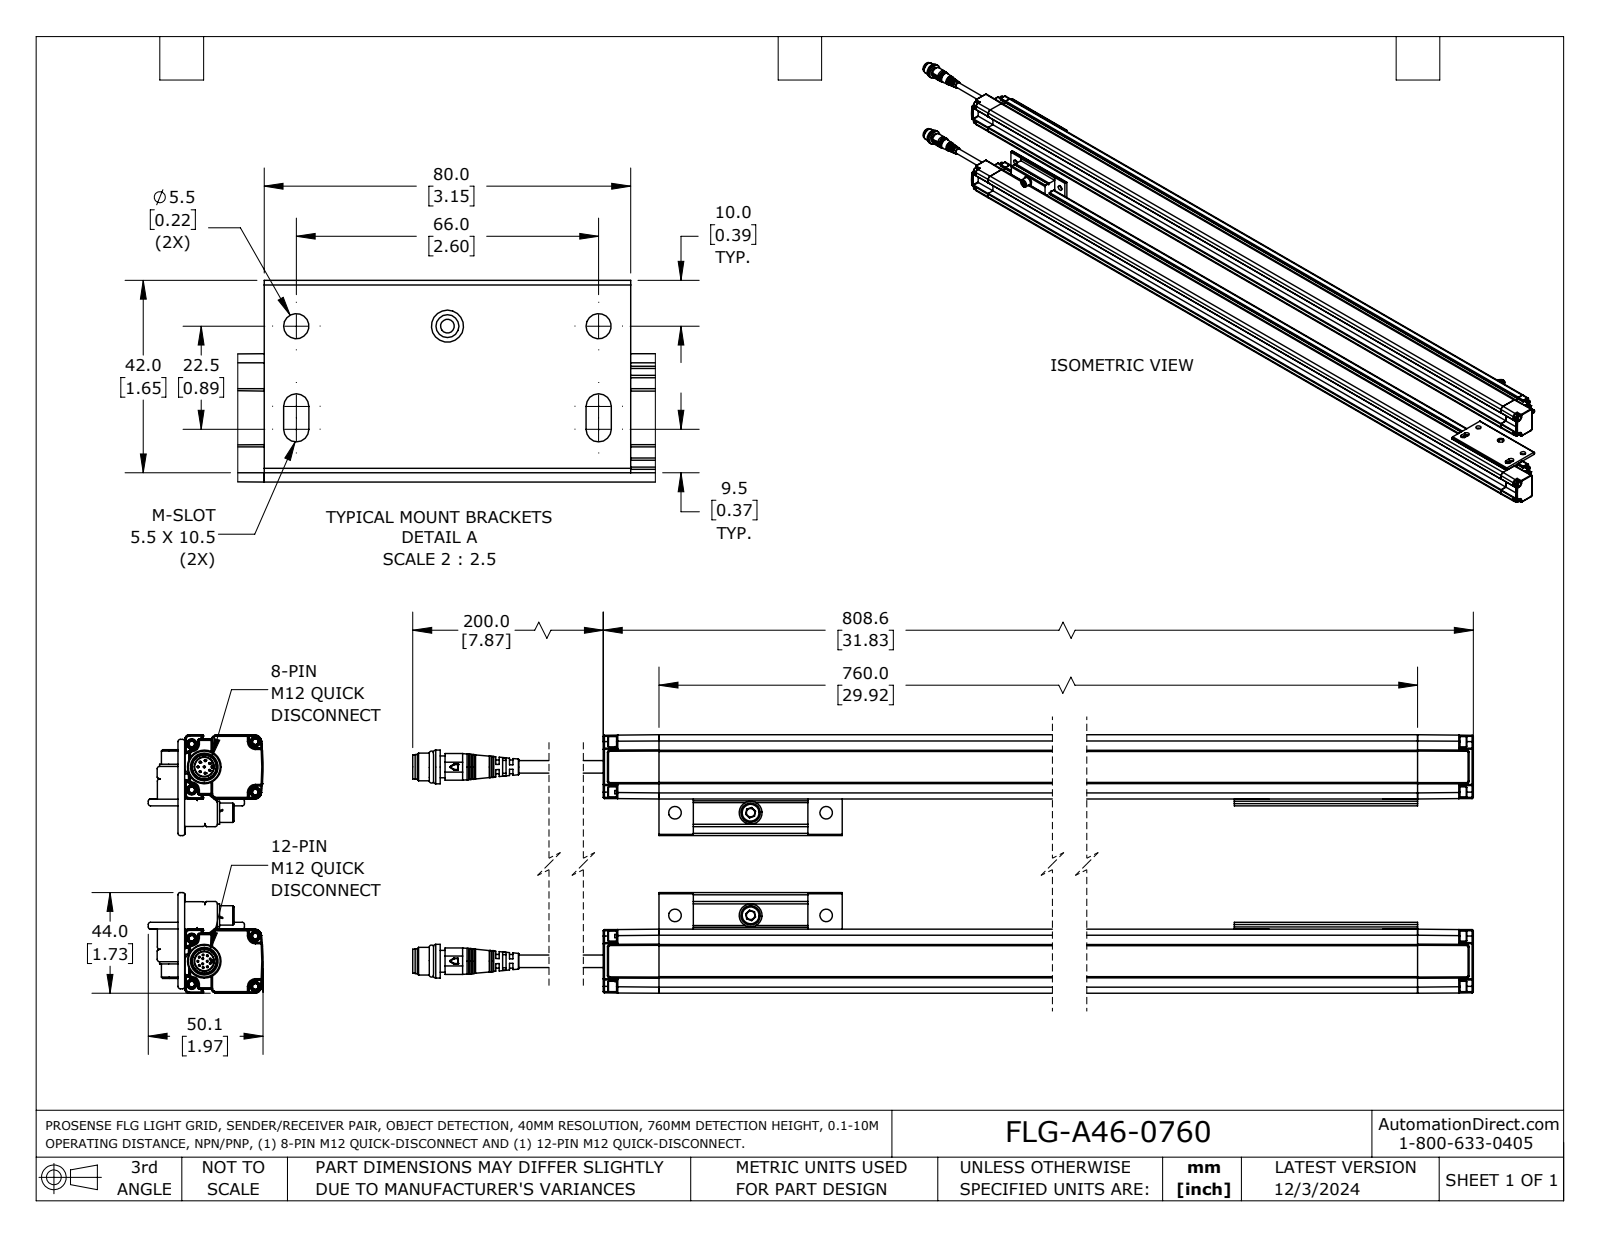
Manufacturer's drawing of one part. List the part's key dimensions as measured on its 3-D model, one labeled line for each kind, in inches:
Part name (STEP PRODUCT): FLG-A46-0760
STEP written by: SolidWorks 2023 (AUTOMOTIVE_DESIGN)
Units: inches
Bodies: 5 solids, 869 faces (435 planar, 238 cylindrical, 196 other)
Overall size (bounding box): 35.455 × 1.972 × 1.732
Volume: 40.48 in³ · Surface area: 264.4 in²
Round holes (diameter × count): ⌀0.016 ×16, ⌀0.217 ×4, ⌀0.098 ×2, ⌀0.197 ×2, ⌀0.327 ×1
Round bosses / shafts (diameter × count): ⌀0.031 ×8, ⌀0.177 ×4, ⌀0.118 ×4, ⌀0.394 ×2, ⌀0.335 ×2, ⌀0.217 ×2, ⌀0.146 ×2, ⌀0.059 ×2
Partial cylindrical surfaces — rounded edges, fillets, slot ends (radius × count): R0.02 ×76, R0.039 ×20, R0.01 ×10, R0.108 ×8, R0.008 ×6, R0.012 ×6, R0.1 ×4, R0.049 ×2
Main face-to-face distances: 1.102, 0.071, 0.817, 0.285, 0.97, 1.041, 0.118, 0.189, 0.215, 1.031
Hole centre spacings: 0.108, 0.163, 1.299, 0.215, 0.089, 0.09, 0.09, 0.118
